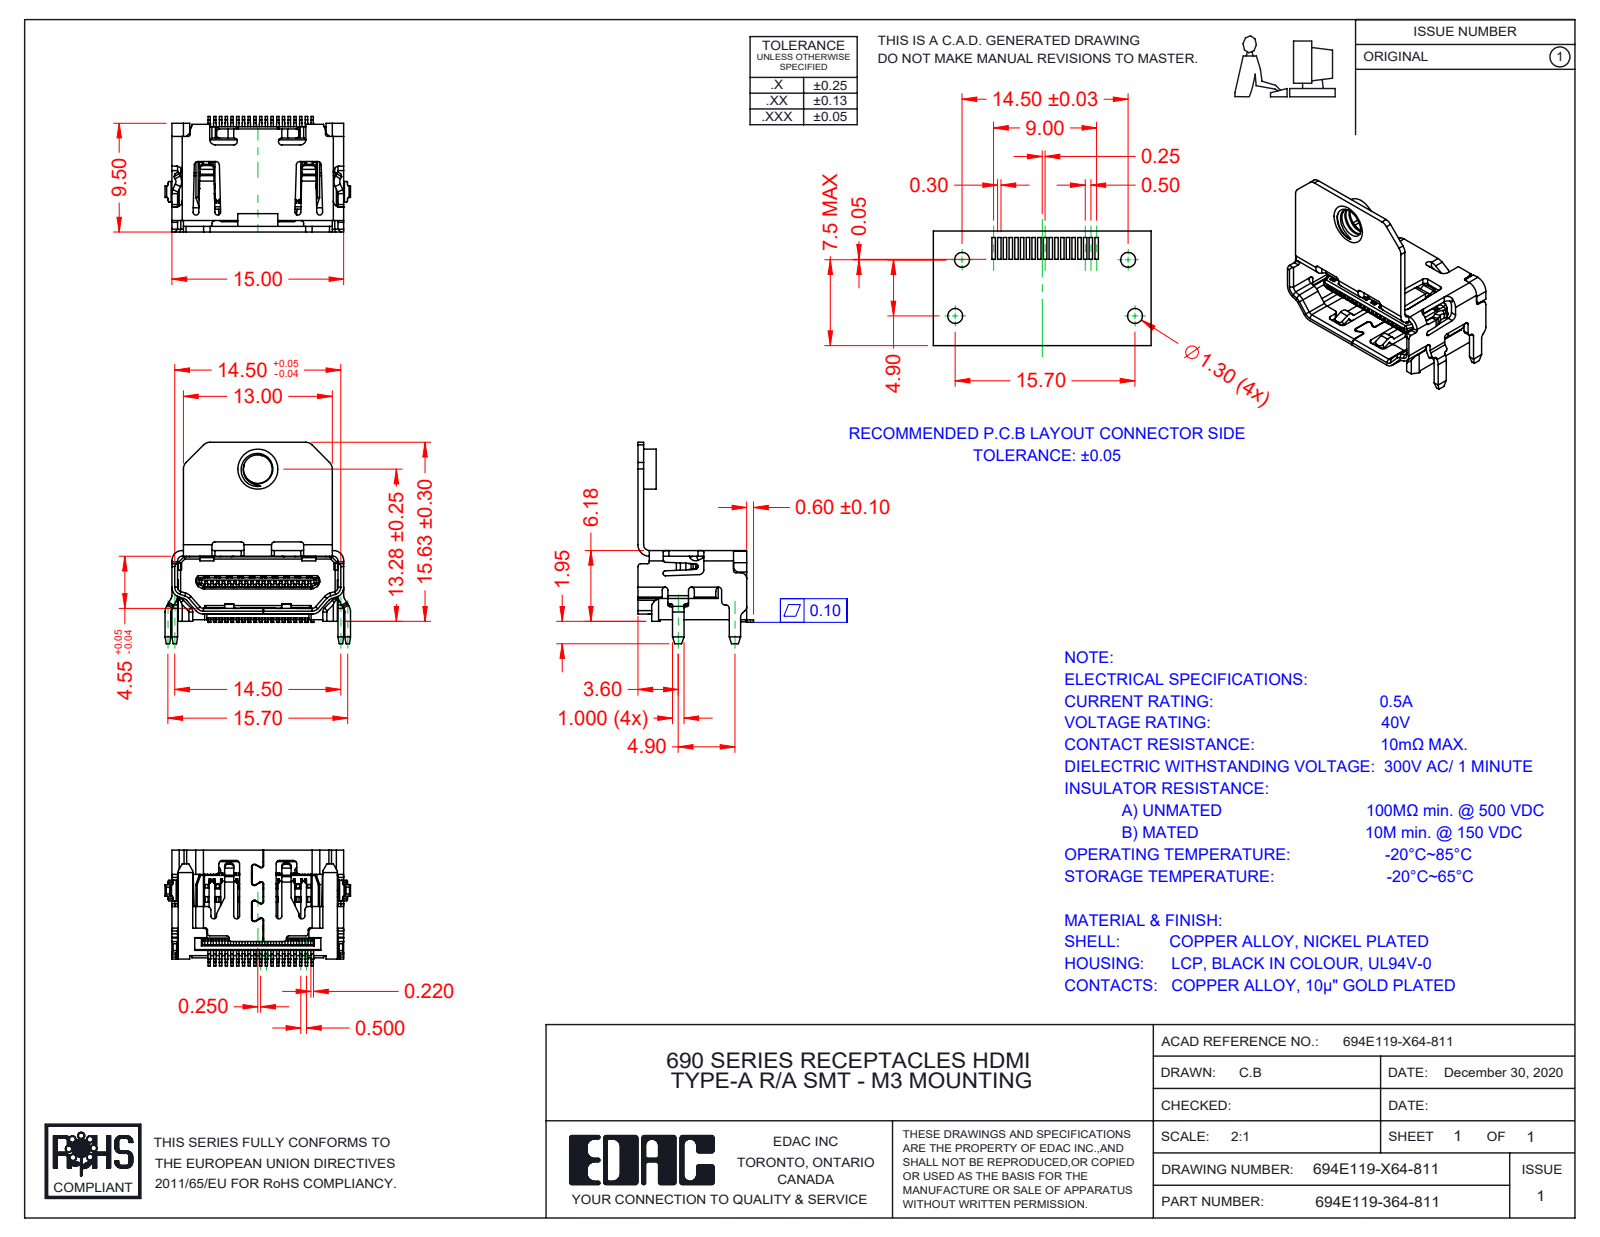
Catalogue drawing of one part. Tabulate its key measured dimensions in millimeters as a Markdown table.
| quantity | value |
| --- | --- |
| part name | Shell 694E119-X64-811; Contact Upper 694E119-X64-811; Insulator 694E119-X64-811; 694E119-164-811 (+1 more) |
| STEP written by | SolidWorks 2020 (AUTOMOTIVE_DESIGN) |
| units | millimeters |
| bodies | 21 solids, 2744 faces (1991 planar, 676 cylindrical, 77 other) |
| overall size | 18.33 × 16.2 × 10.1 |
| volume | 405 mm³ |
| surface area | 1 700 mm² |
| round holes (diameter × count) | 2.5 × 1 |
| round bosses / shafts (diameter × count) | 3.5 × 1 |
| partial cylindrical surfaces (radius × count) | 0.2 × 47, 0.25 × 32, 0.3 × 26, 0.5 × 24, 0.15 × 23, 1 × 13, 0.4 × 10, 0.35 × 8 |
| main face-to-face distances | 0.5, 2.52, 2.02, 5.04, 3.02, 8.7, 9.2, 0.55, 2.4, 6.3 |
